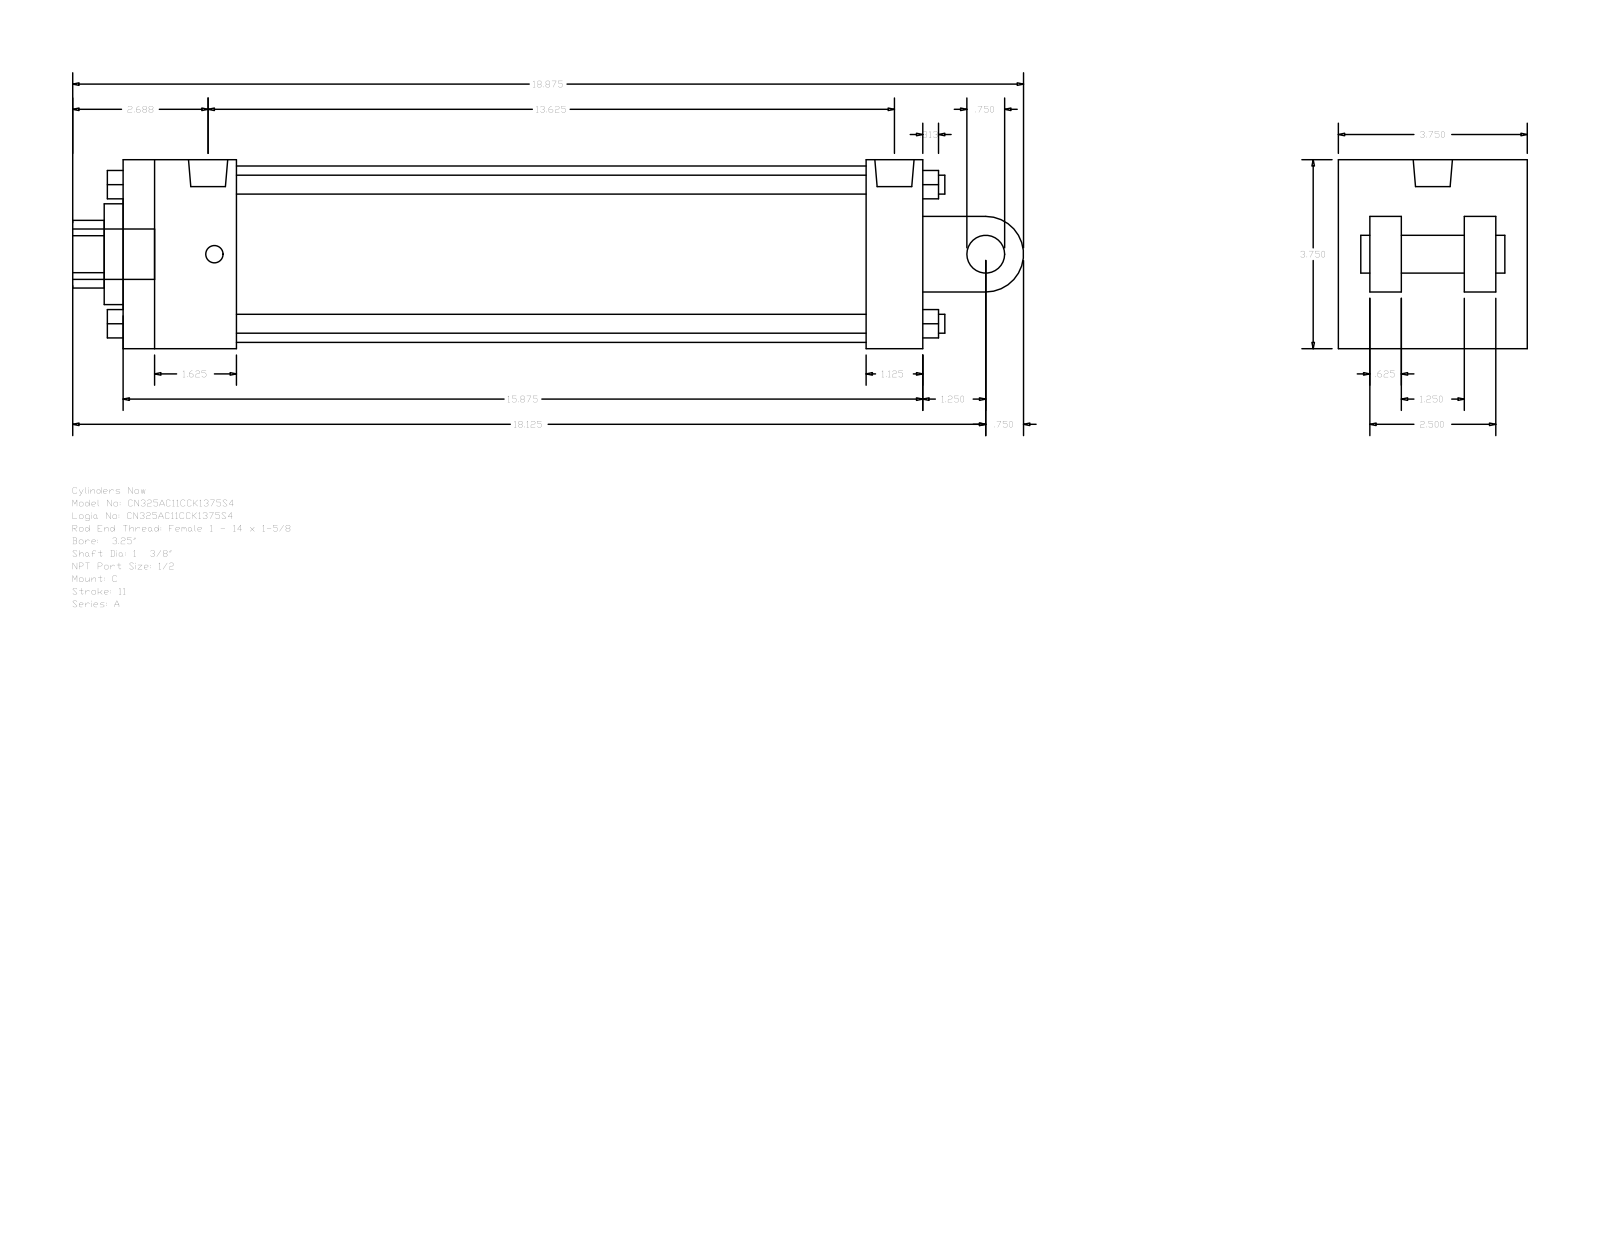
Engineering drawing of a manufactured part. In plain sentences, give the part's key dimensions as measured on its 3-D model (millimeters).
The part is named "A_C__0325_1.375". Its 3-D file was written by "GSSL Pune (CONFIG_CONTROL_DESIGN)". It is 0 solids with 135 faces: 102 planar, 33 cylindrical and 0 other. Overall it measures 479.43 by 95.25 by 95.25 millimeters. Round holes: 2 of diameter 8.73, 1 of diameter 19.77, 1 of diameter 34.92, 1 of diameter 50.8, 1 of diameter 88.9. Round bosses or shafts: 4 of diameter 9.53, 2 of diameter 8.73, 1 of diameter 25.4, 1 of diameter 19.77, 1 of diameter 19.05. Partial cylindrical surfaces (rounded edges, fillets, slot ends): 1 of radius 17.06, 1 of radius 19.05. The main face-to-face distances are 95.24, 15.87, 403.22, 28.57, 63.5, 66.67, 79.37, 31.74, 47.63, 374.65. The hole center spacings are 3.18.
